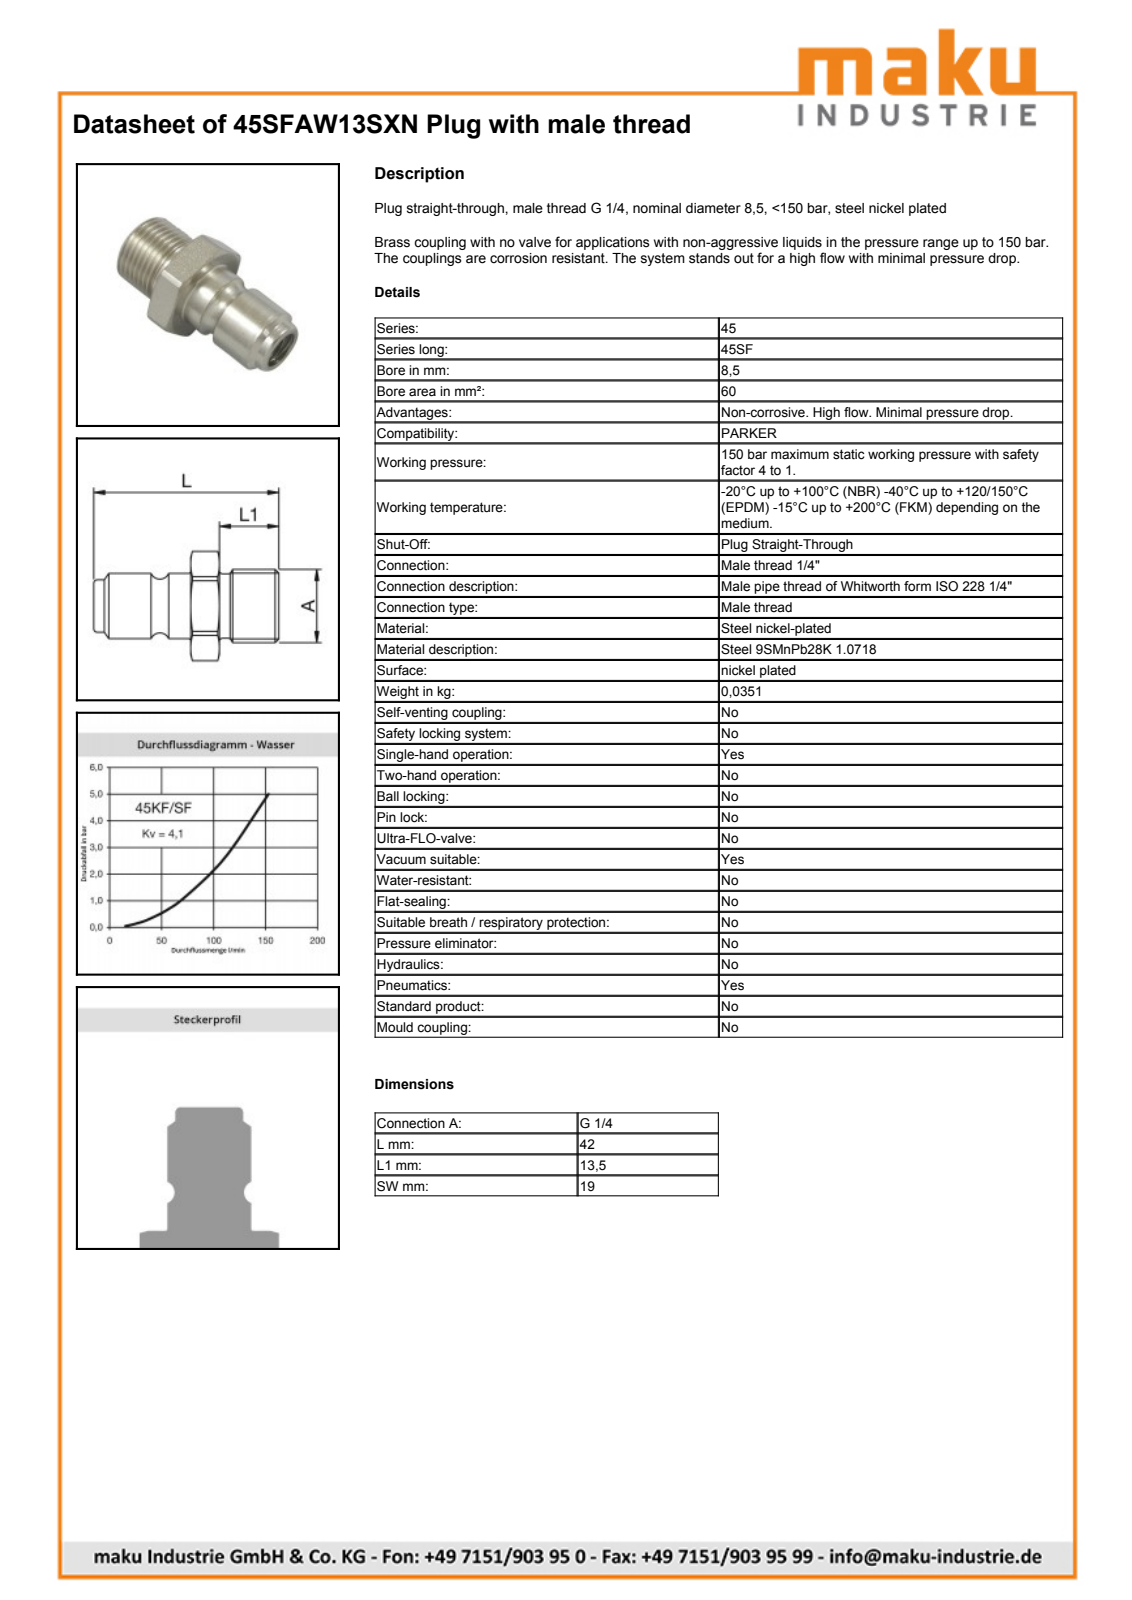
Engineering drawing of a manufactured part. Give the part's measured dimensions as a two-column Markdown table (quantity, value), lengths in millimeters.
| quantity | value |
| --- | --- |
| part name | D107779 |
| STEP written by | Autodesk Inventor 2013 (AUTOMOTIVE_DESIGN) |
| units | millimeters |
| bodies | 1 solid, 42 faces (10 planar, 12 cylindrical, 20 other) |
| overall size | 42 × 21.4 × 19 |
| volume | 4 816 mm³ |
| surface area | 3 567 mm² |
| round holes (diameter × count) | 8.5 × 1 |
| round bosses / shafts (diameter × count) | 14.8 × 1, 13.16 × 1, 11.9 × 1, 11.2 × 1 |
| partial cylindrical surfaces (radius × count) | 10.7 × 1 |
| main face-to-face distances | 19, 6.5, 20, 13.5, 22, 28.5, 42 |
